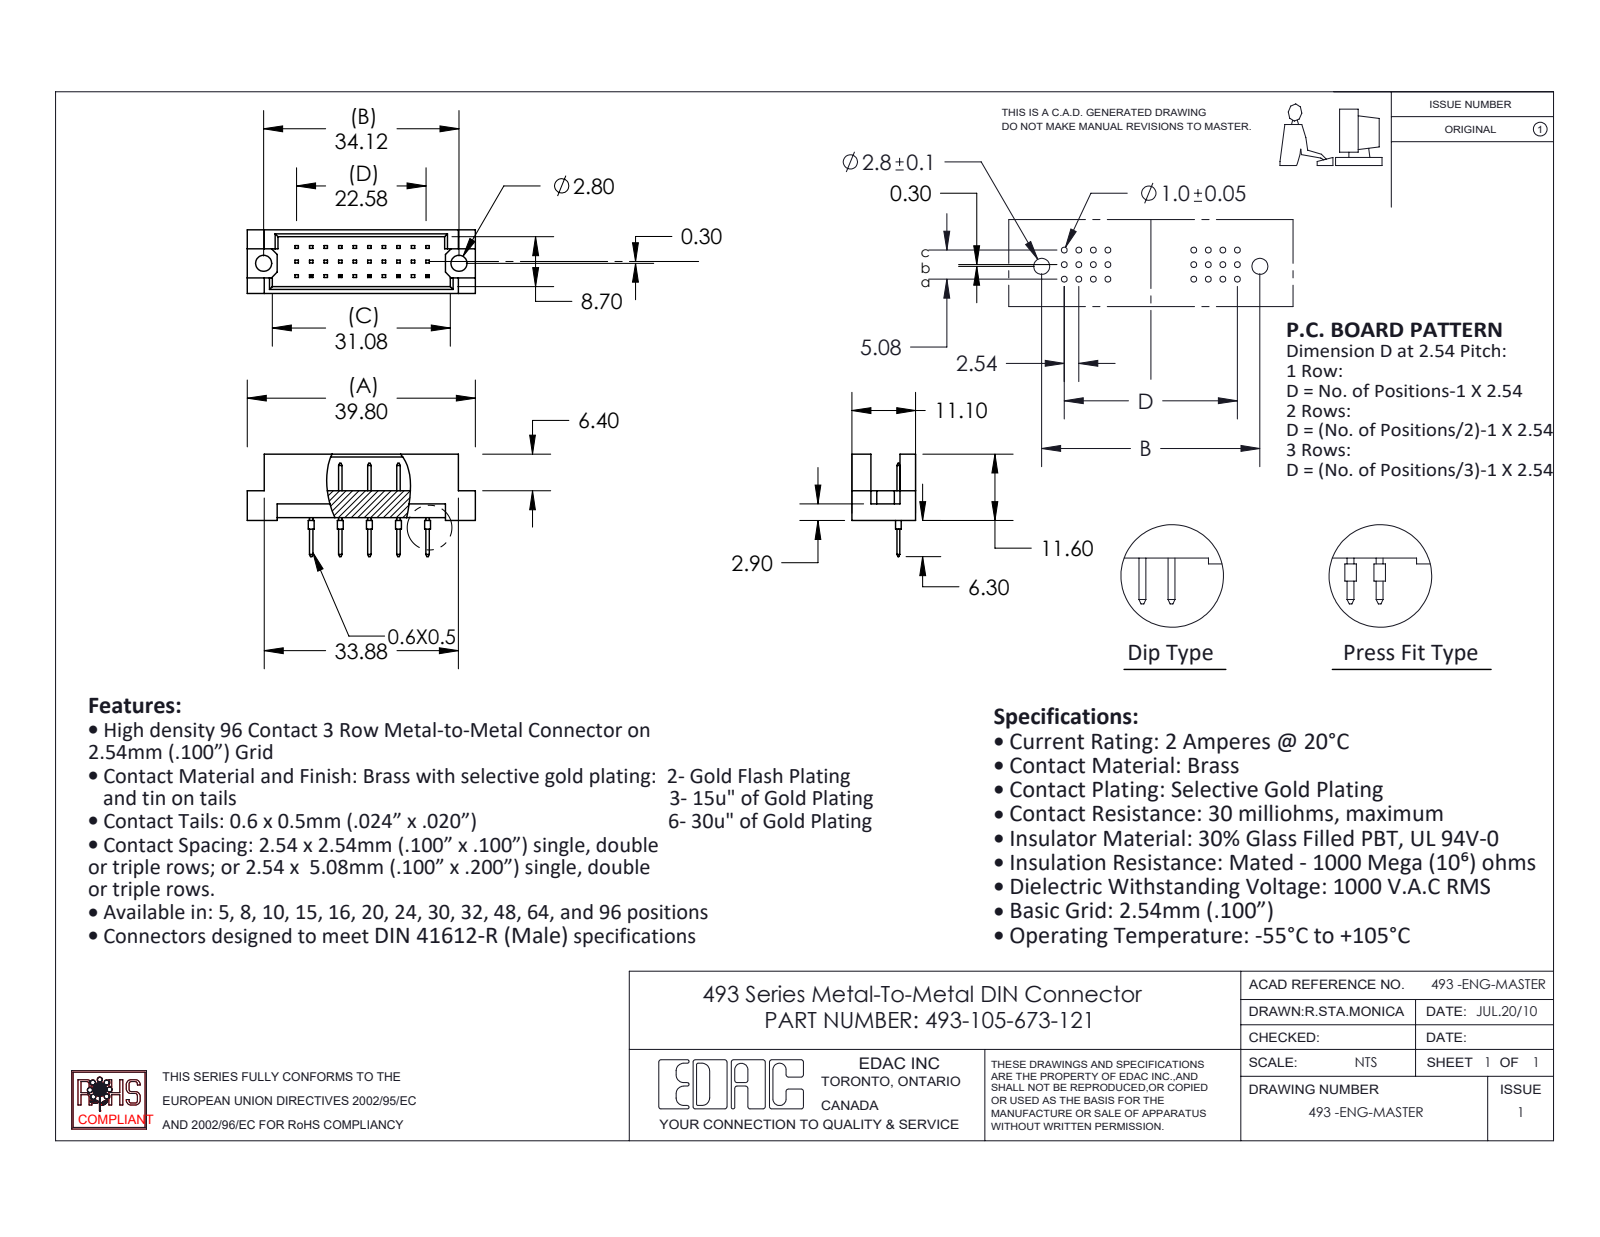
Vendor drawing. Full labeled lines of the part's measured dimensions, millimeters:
Part name (STEP PRODUCT): 493-290_73; 493-105-673-121; 493 Part_30
STEP written by: SolidWorks 2020 (CONFIG_CONTROL_DESIGN)
Units: millimetres
Bodies: 6 solids, 282 faces (268 planar, 14 cylindrical, 0 other)
Overall size (bounding box): 39.8 × 17.9 × 11.1
Volume: 2 401 mm³ · Surface area: 2 927 mm²
Round holes (diameter × count): ⌀2.8 ×2
Round bosses / shafts (diameter × count): ⌀1 ×5
Main face-to-face distances: 1.2, 9.9, 11.1, 8.7, 4.7, 0.5, 5.08, 2.4, 2.54, 2.3
Hole centre spacings: 34.12
